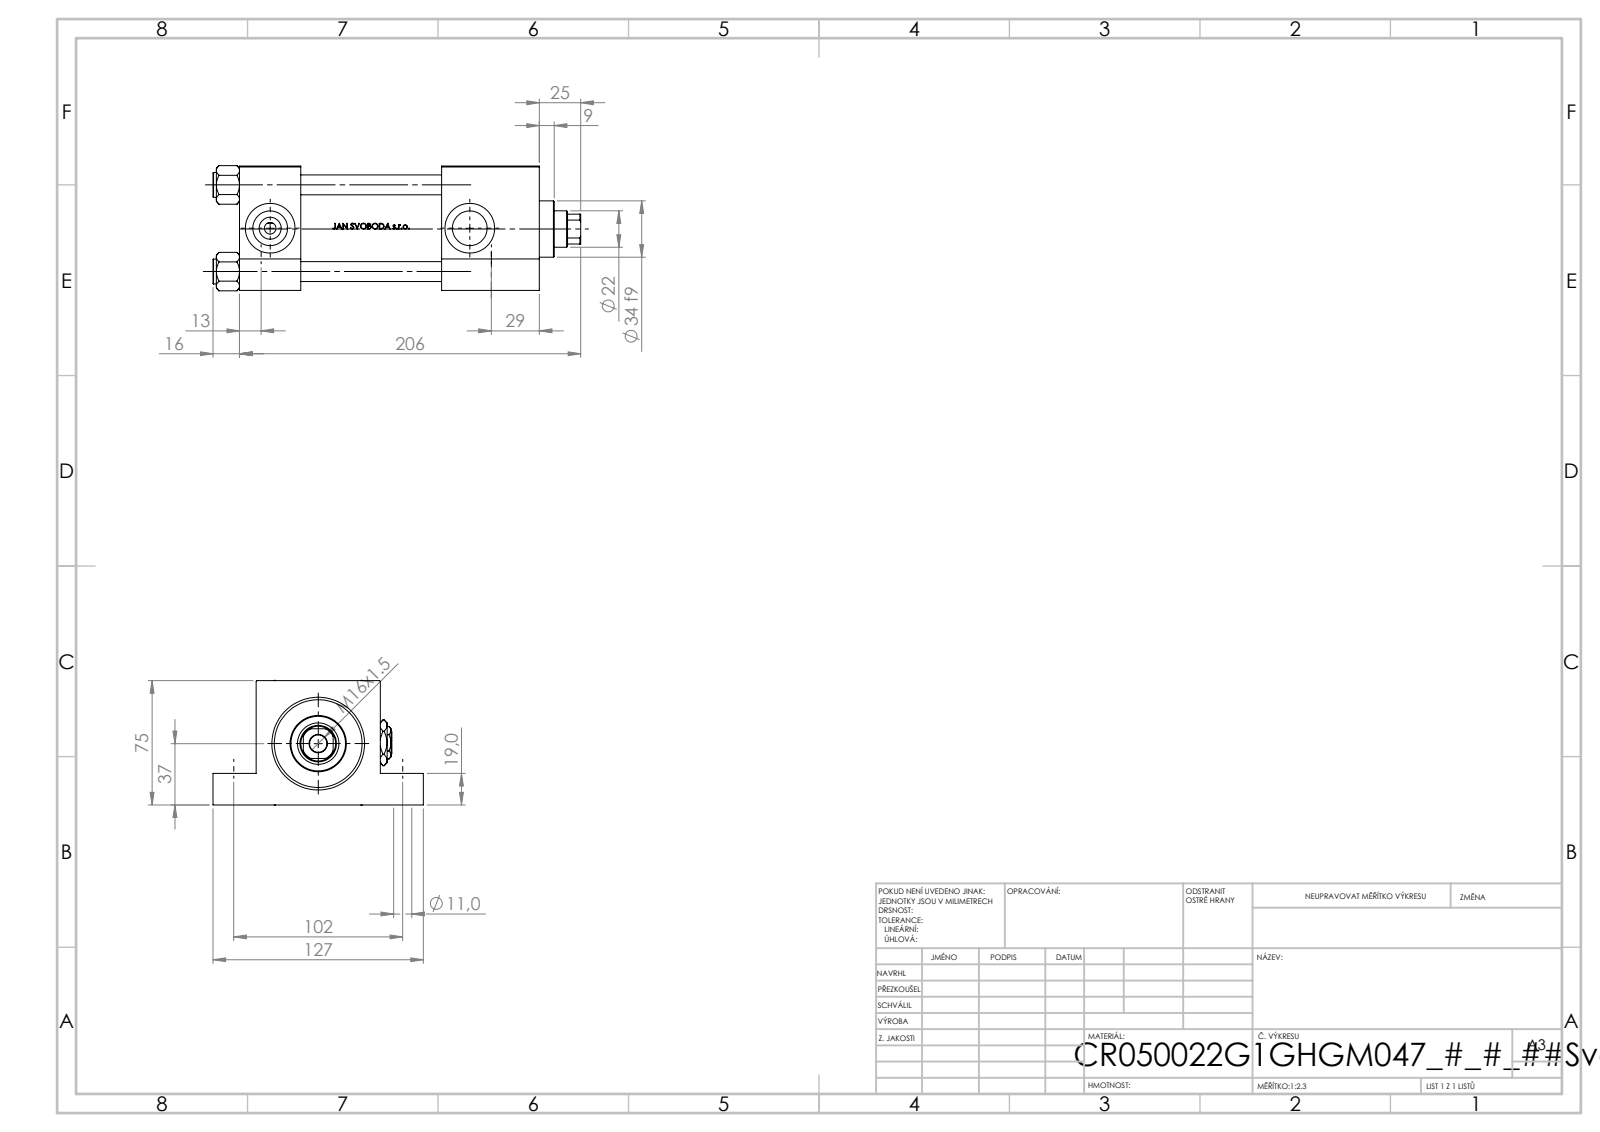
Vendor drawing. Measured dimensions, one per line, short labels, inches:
name: V215CR_G_Body; NUT_M5_G; V215_VC_A; V215CR_VCP_G (+2 more)
written by: SolidWorks 2019 (CONFIG_CONTROL_DESIGN)
unit: in
bodies: 12 solids, 1134 faces (454 planar, 128 cylindrical, 552 other)
size: 8.74 × 5 × 2.974
volume: 48.11 in³; area: 273.2 in²
holes: 4× ⌀0.433, 4× ⌀0.472, 2× ⌀0.276, 2× ⌀0.825, 2× ⌀1.181, 1× ⌀0.413, 1× ⌀0.866, 1× ⌀0.984, 1× ⌀1.614, 1× ⌀1.969, 1× ⌀2.087
bosses: 4× ⌀0.591, 1× ⌀2.205, 1× ⌀1.339
rounds: 1× R0.413
face distances: 2.953, 1.457, 7.126, 5.669, 0.748, 2.205, 4.803, 3.346, 2.323, 1.024
hole spacings: 2.059, 1.442, 1.47, 2.912, 4.016, 5.472, 6.788, 4.744
